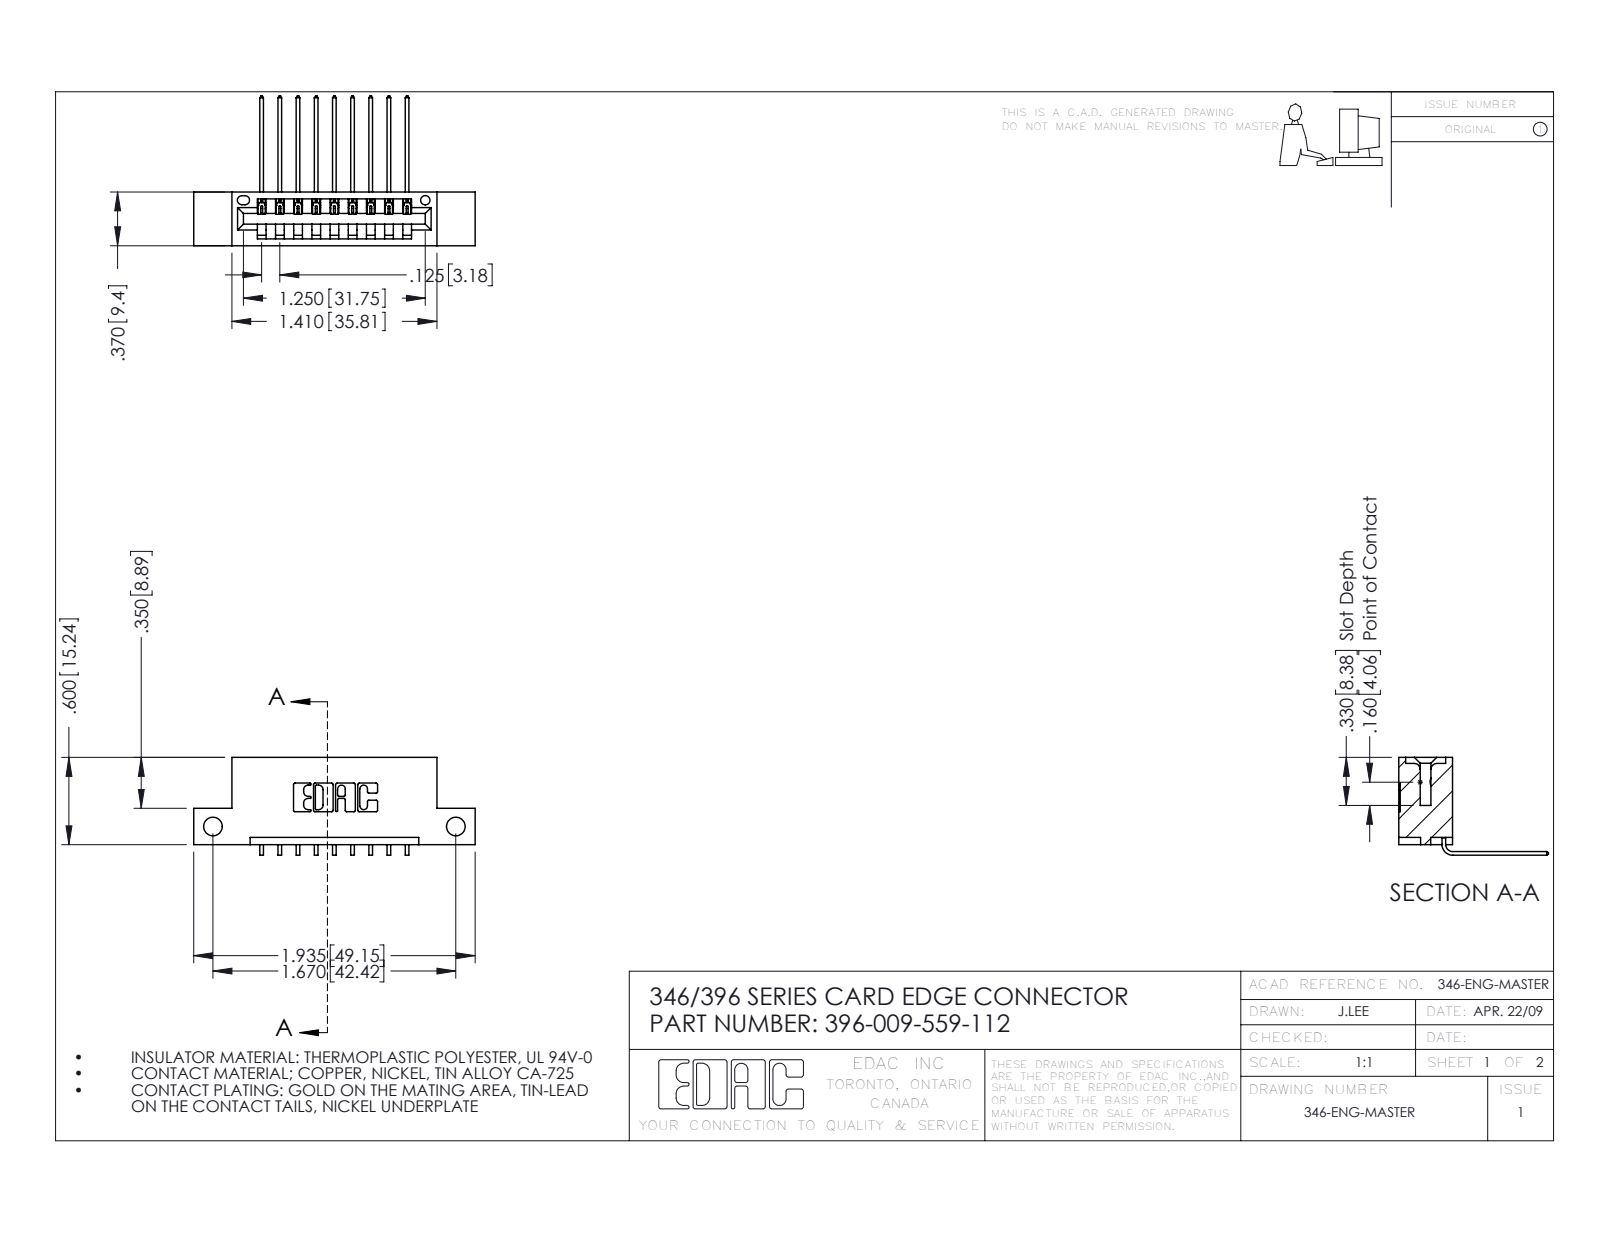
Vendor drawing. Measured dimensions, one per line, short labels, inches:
name: 346 Part_Flush Mounting Lugs - Side Mount; 345-292-001_558 559 Tail - 1; 396-009-559-112
written by: SolidWorks 2016 (CONFIG_CONTROL_DESIGN)
unit: in
bodies: 10 solids, 662 faces (454 planar, 208 cylindrical, 0 other)
size: 1.935 × 1.03 × 0.673
volume: 0.27 in³; area: 8.062 in²
holes: 2× ⌀0.128, 1× ⌀0.064
rounds: 22× R0.01, 18× R0.006, 6× R0.007, 6× R0.031, 3× R0.026, 2× R0.031, 2× R0.04, 1× R0.014
face distances: 0.25, 0.048, 0.322, 0.37, 0.072, 0.298, 0.025, 0.148, 0.222, 0.1
hole spacings: 1.67
